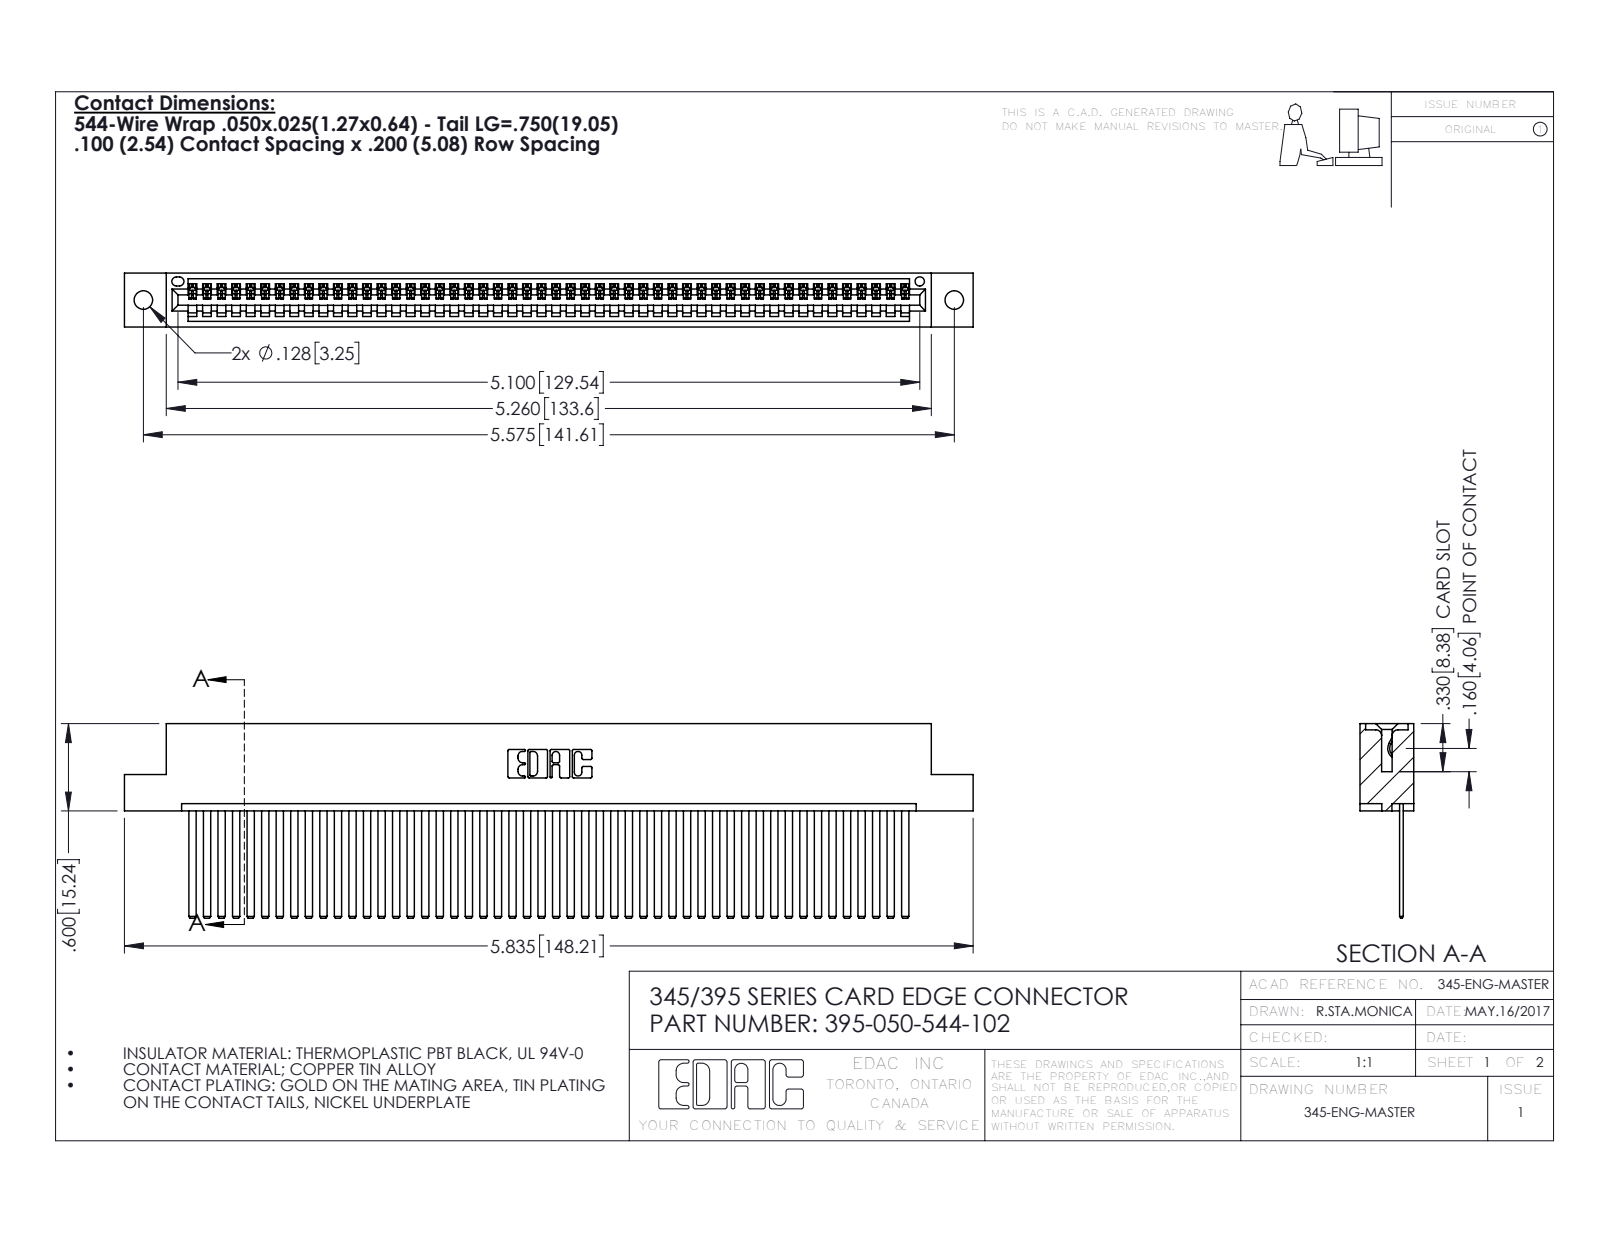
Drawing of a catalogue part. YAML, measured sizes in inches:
part_name: "395-050-544-102; 345-292-001_345-293-144; 345 Part_Flush Mounting Lugs - 0.128 Dia"
step_written_by: "SolidWorks 2016 (CONFIG_CONTROL_DESIGN)"
units: inches
bodies: {solids: 51, faces: 2726, planar: 1880, cylindrical: 846, other: 0}
overall_size: [5.835, 1.337, 0.37]
volume: 0.896
surface_area: 32.69
round_holes:
  - {diameter: 0.128, count: 2}
  - {diameter: 0.064, count: 1}
partial_cylinders:
  - {radius: 0.006, count: 100}
  - {radius: 0.01, count: 22}
  - {radius: 0.007, count: 6}
  - {radius: 0.031, count: 6}
  - {radius: 0.026, count: 3}
  - {radius: 0.031, count: 2}
  - {radius: 0.04, count: 2}
  - {radius: 0.014, count: 1}
face_to_face_distances: [0.072, 0.298, 0.025, 0.098, 0.272, 0.37, 0.2, 0.225, 0.149, 0.072]
hole_center_spacings: [0.27, 5.339, 5.575]
